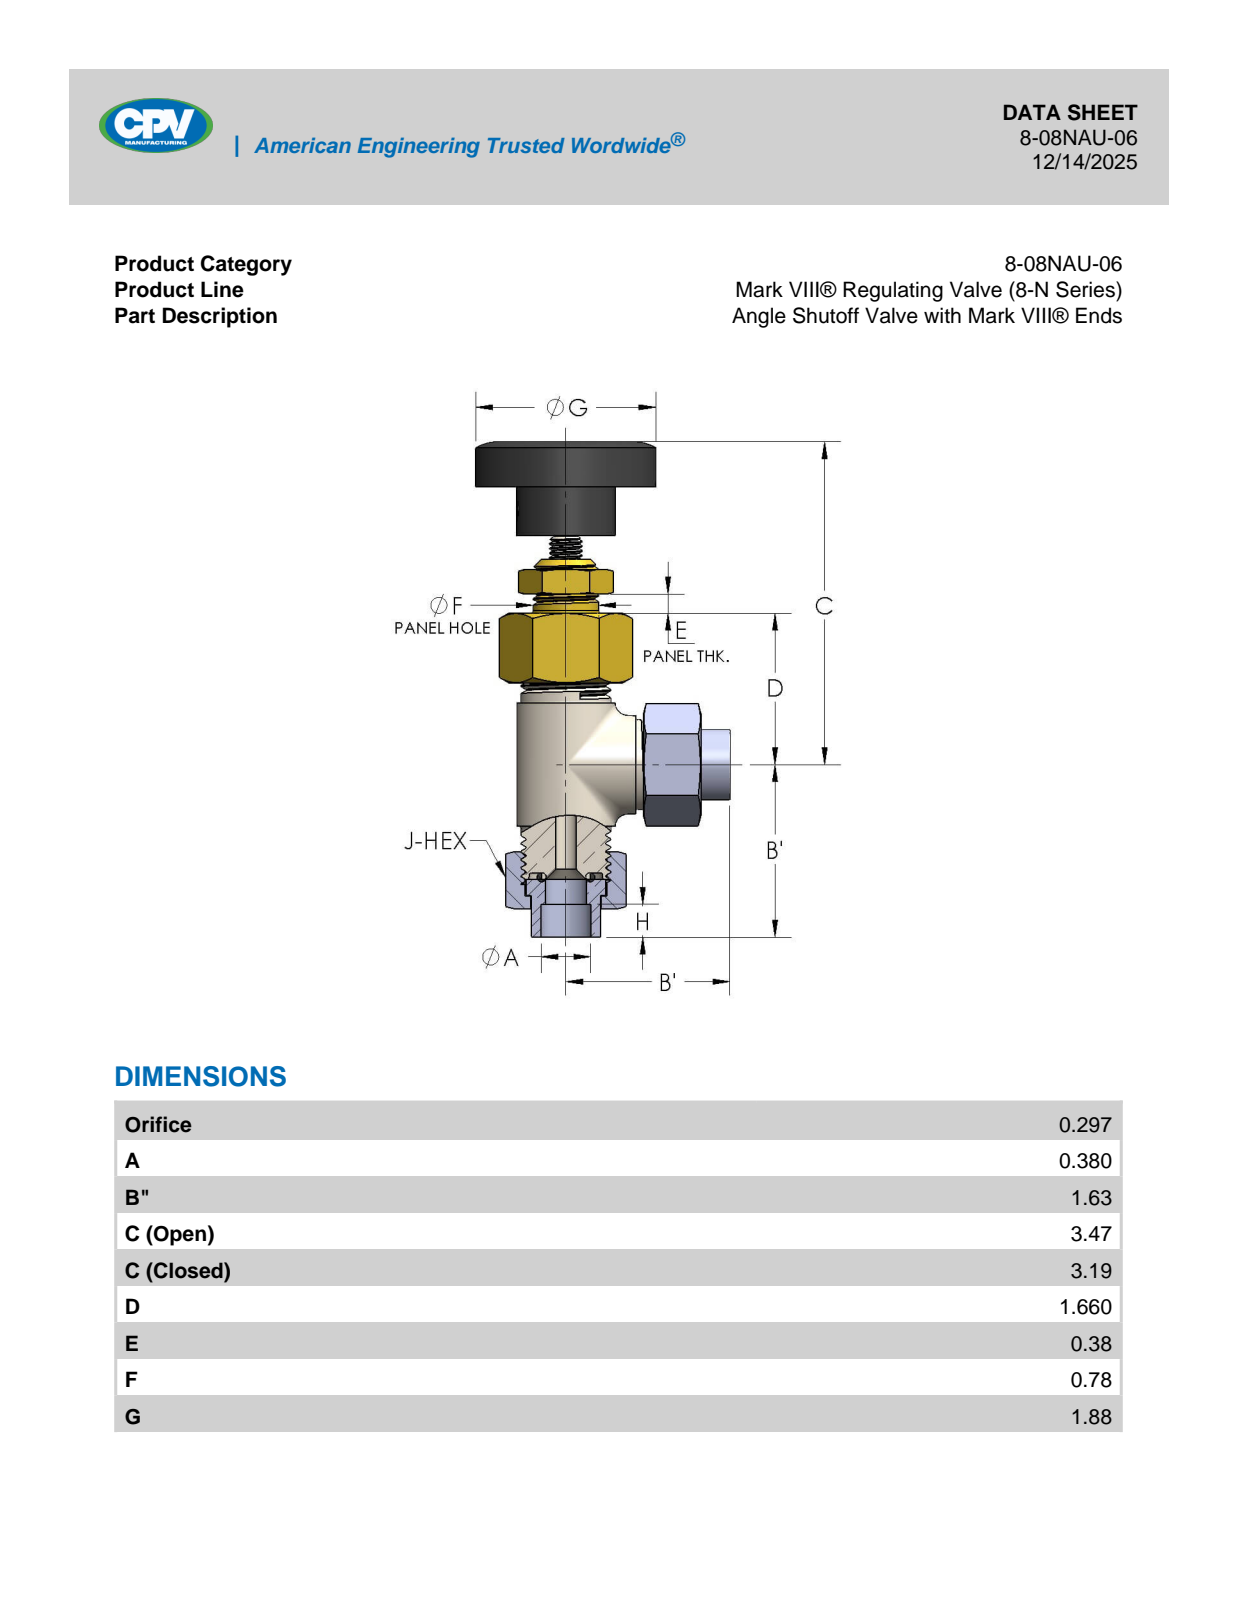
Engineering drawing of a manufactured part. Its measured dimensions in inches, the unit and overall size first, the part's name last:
Units: inches
Overall size (bounding box): 4.835 × 2.568 × 1.88
Round holes (diameter × count): ⌀0.344 ×2, ⌀0.38 ×2, ⌀0.252 ×1
Round bosses / shafts (diameter × count): ⌀0.808 ×2, ⌀0.59 ×2, ⌀1.88 ×1, ⌀1 ×1, ⌀0.996 ×1, ⌀0.748 ×1, ⌀0.312 ×1, ⌀0.25 ×1
Main face-to-face distances: 1.125, 0.31, 1.035, 0.095, 0.5, 0.093, 1.032, 1.128, 1.13, 0.095
Volume: 5.513 in³ · Surface area: 33.08 in²
Bodies: 1 solid, 178 faces (60 planar, 44 cylindrical, 74 other)
Part name (STEP PRODUCT): 8-08SAU-06
STEP written by: SolidWorks 2018 (AUTOMOTIVE_DESIGN)
